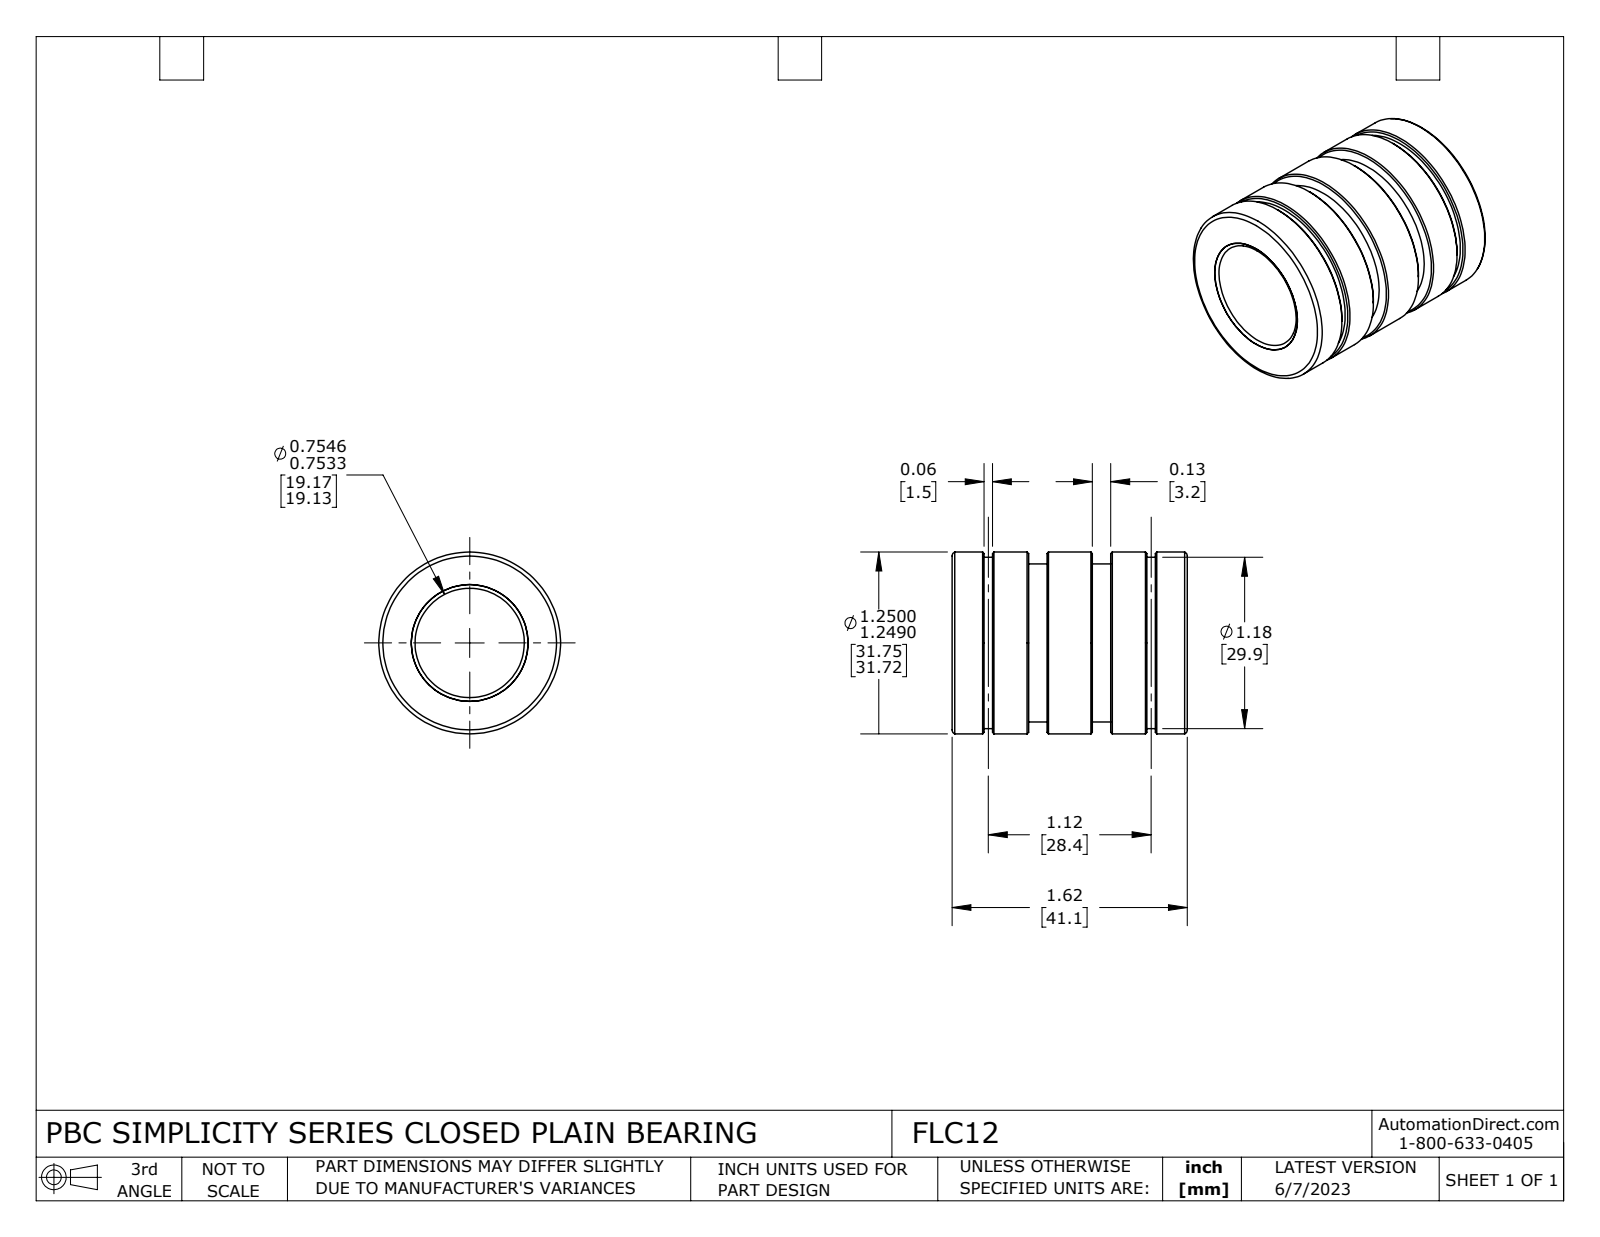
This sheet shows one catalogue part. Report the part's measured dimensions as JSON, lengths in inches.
{"part_name": "FLC12", "step_written_by": "SolidWorks 2021 (CONFIG_CONTROL_DESIGN)", "units": "inches", "bodies": {"solids": 2, "faces": 58, "planar": 10, "cylindrical": 24, "other": 24}, "overall_size": [1.618, 1.249, 1.249], "volume_in3": 1.171, "surface_area_in2": 21.14, "round_holes": [[0.751, 1], [0.802, 1]], "round_bosses_or_shafts": [[1.249, 1], [1.177, 1], [1.087, 1]], "face_to_face_distances": [1.617, 0.527, 1.091, 0.653, 0.965, 0.126, 0.438, 0.564, 0.312, 0.278]}
